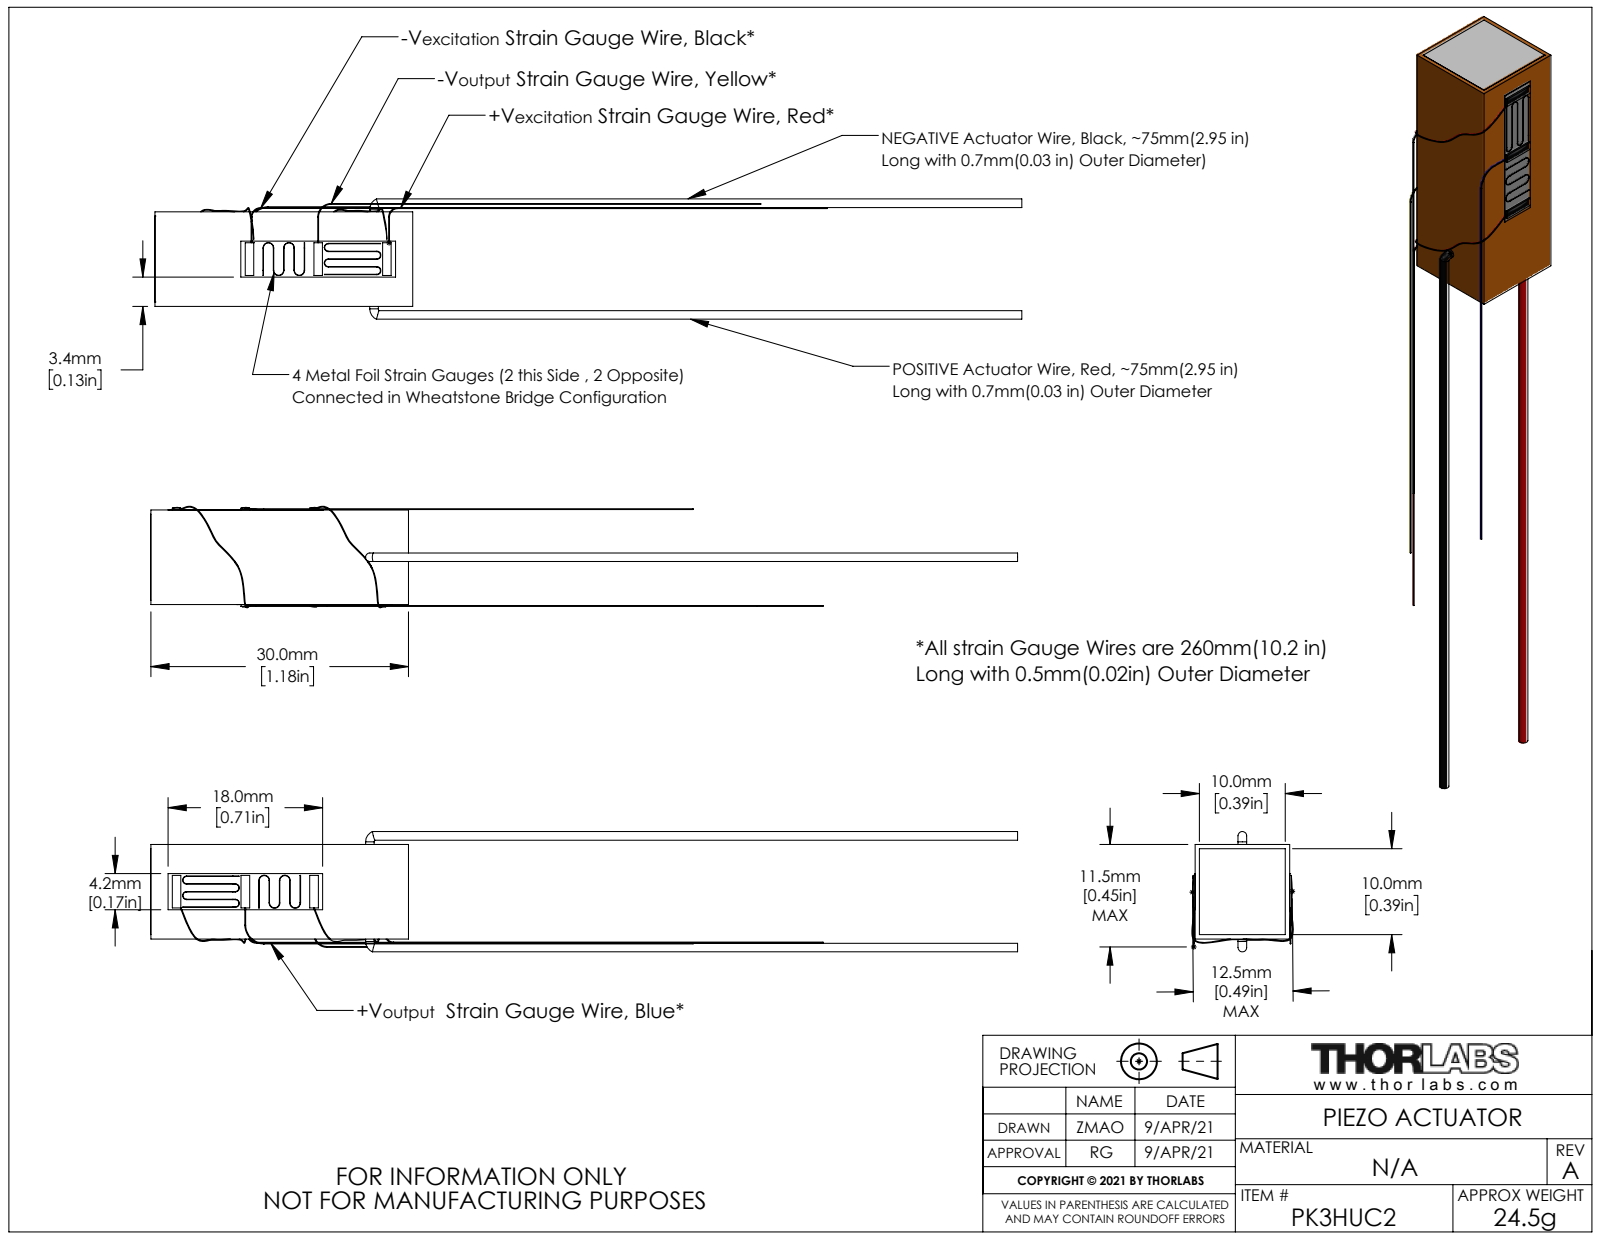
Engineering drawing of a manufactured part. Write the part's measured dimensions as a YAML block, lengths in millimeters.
part_name: "CTN016914-E0W"
step_written_by: "SolidWorks 2018 (AUTOMOTIVE_DESIGN)"
units: millimeters
bodies: {solids: 2, faces: 172, planar: 69, cylindrical: 57, other: 46}
overall_size: [100.92, 14, 11.81]
volume: 3759
surface_area: 2130
round_bosses_or_shafts:
  - {diameter: 1, count: 3}
face_to_face_distances: [11, 11.01, 30, 11.02, 30.01, 29.99, 8, 1, 10.5, 9]
